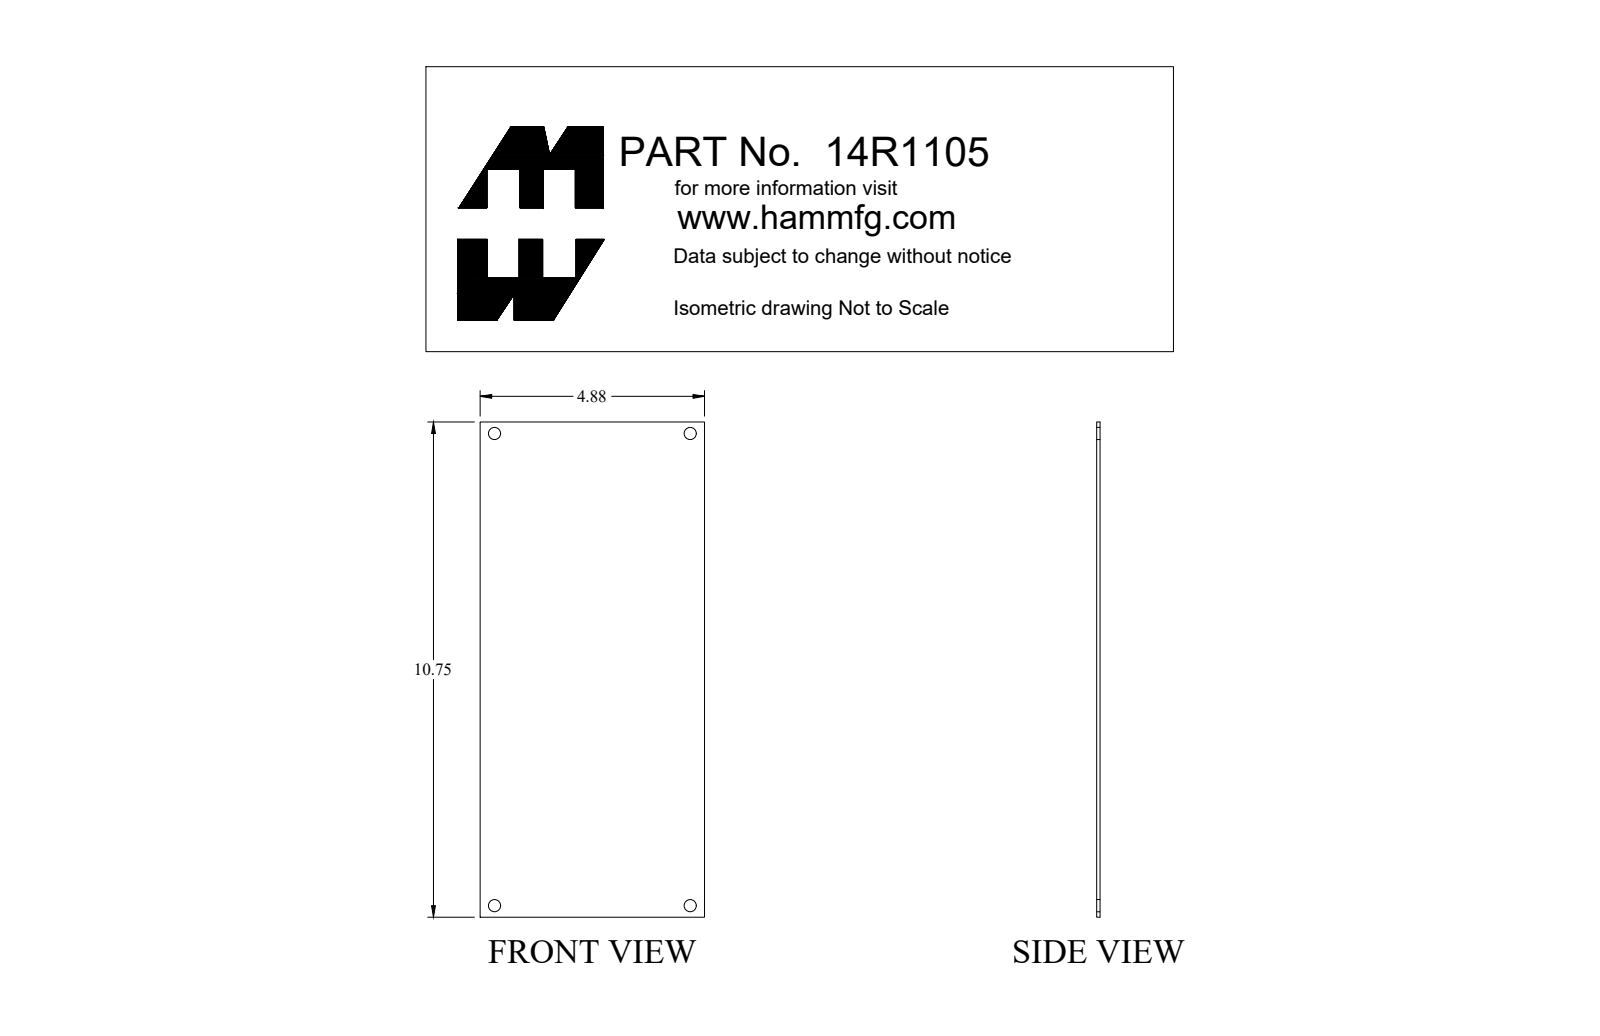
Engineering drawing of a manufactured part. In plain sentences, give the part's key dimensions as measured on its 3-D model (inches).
The part is named "14R1105". Its 3-D file was written by "SolidWorks 2018 (AUTOMOTIVE_DESIGN)". It is 1 solid with 10 faces: 6 planar, 4 cylindrical and 0 other. Overall it measures 10.75 by 4.875 by 0.072 inches. Its volume is 3.757 cubic inches and its surface area 106.9 square inches. Round holes: 4 of diameter 0.265. The main face-to-face distances are 0.072, 4.875, 10.75. The hole center spacings are 4.25, 10.25, 11.096.
